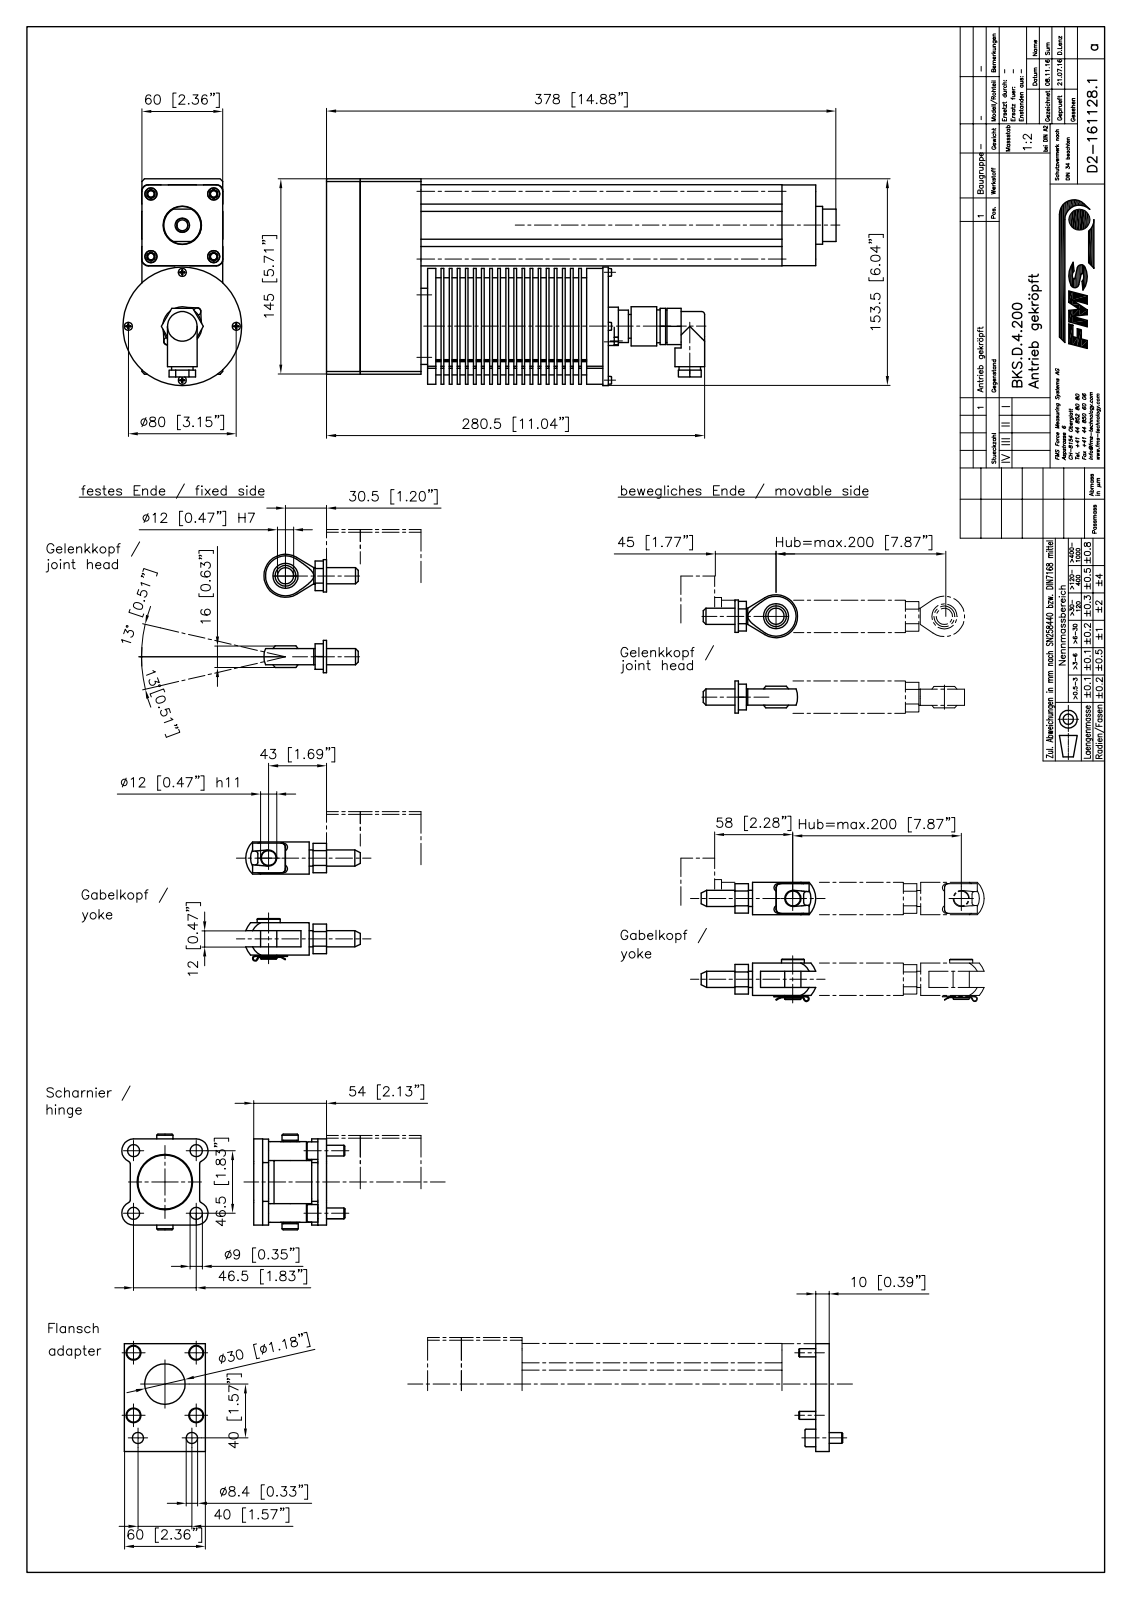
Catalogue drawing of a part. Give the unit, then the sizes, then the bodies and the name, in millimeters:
Units: millimetres
Overall size (bounding box): 471 × 153.5 × 88
Round holes (diameter × count): ⌀2.6 ×10, ⌀3.42 ×8, ⌀5.15 ×8, ⌀5 ×5, ⌀4 ×4, ⌀6.3 ×4, ⌀6.4 ×4, ⌀6.65 ×4, ⌀6.91 ×4, ⌀9 ×4, ⌀2.14 ×3, ⌀3.6 ×2
Round bosses / shafts (diameter × count): ⌀2.15 ×7, ⌀3 ×6, ⌀10 ×4, ⌀6 ×4, ⌀24 ×2, ⌀5.5 ×2, ⌀88 ×1, ⌀86 ×1
Partial cylindrical surfaces — rounded edges, fillets, slot ends (radius × count): R5 ×18, R0.5 ×14, R8 ×8, R2 ×6, R3 ×6, R20 ×5, R1.75 ×4, R4.5 ×4
Main face-to-face distances: 60.15, 60.3, 60, 70, 56.4, 1.95, 58.35, 1.8, 58.2, 4
Hole centre spacings: 28.73, 67.77, 32.88, 7.63, 21.82, 29.83, 30, 33.3
Volume: 1 421 000 mm³ · Surface area: 495 143 mm²
Bodies: 29 solids, 1266 faces (585 planar, 512 cylindrical, 169 other)
Part name (STEP PRODUCT): K1611281_STP; K1309121; K0702222; K0804232 (+8 more)
STEP written by: Mechanical Desktop 2009 (CONFIG_CONTROL_DESIGN)
